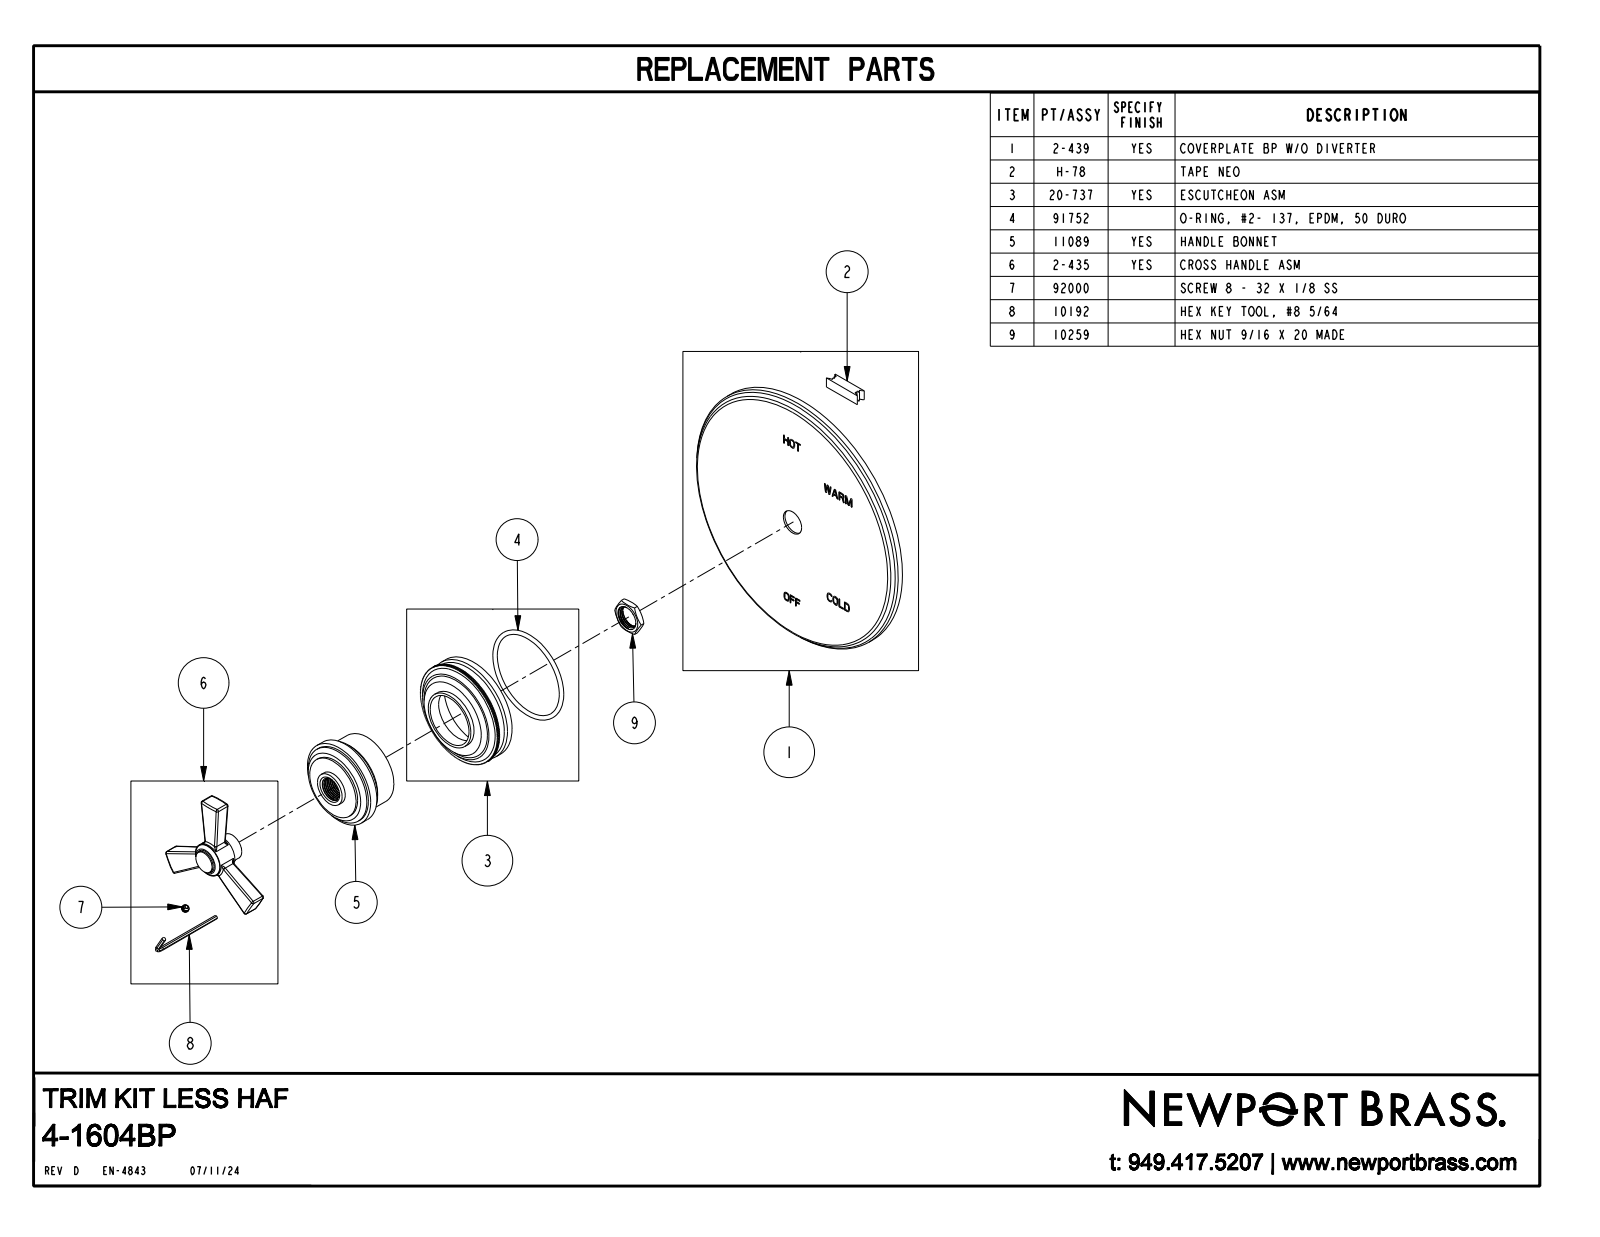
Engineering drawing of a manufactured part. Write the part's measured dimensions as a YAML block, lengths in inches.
part_name: "4-1604BP"
step_written_by: "CREO PARAMETRIC BY PTC INC, 2018400 (CONFIG_CONTROL_DESIGN)"
units: inches
bodies: {solids: 1, faces: 1026, planar: 712, cylindrical: 218, other: 96}
overall_size: [6.5, 6.5, 3.131]
volume: 16.9
surface_area: 92.03
round_bosses_or_shafts:
  - {diameter: 6.5, count: 1}
  - {diameter: 2.5, count: 1}
  - {diameter: 2.4, count: 1}
  - {diameter: 2.05, count: 1}
  - {diameter: 1.9, count: 1}
  - {diameter: 1.75, count: 1}
  - {diameter: 1.5, count: 1}
  - {diameter: 0.8, count: 1}
partial_cylinders:
  - {radius: 0.04, count: 6}
  - {radius: 0.1, count: 6}
face_to_face_distances: [0.313, 2.088, 1.775, 0.2, 0.1, 1.3, 0.15, 0.4, 1.375, 0.9]
